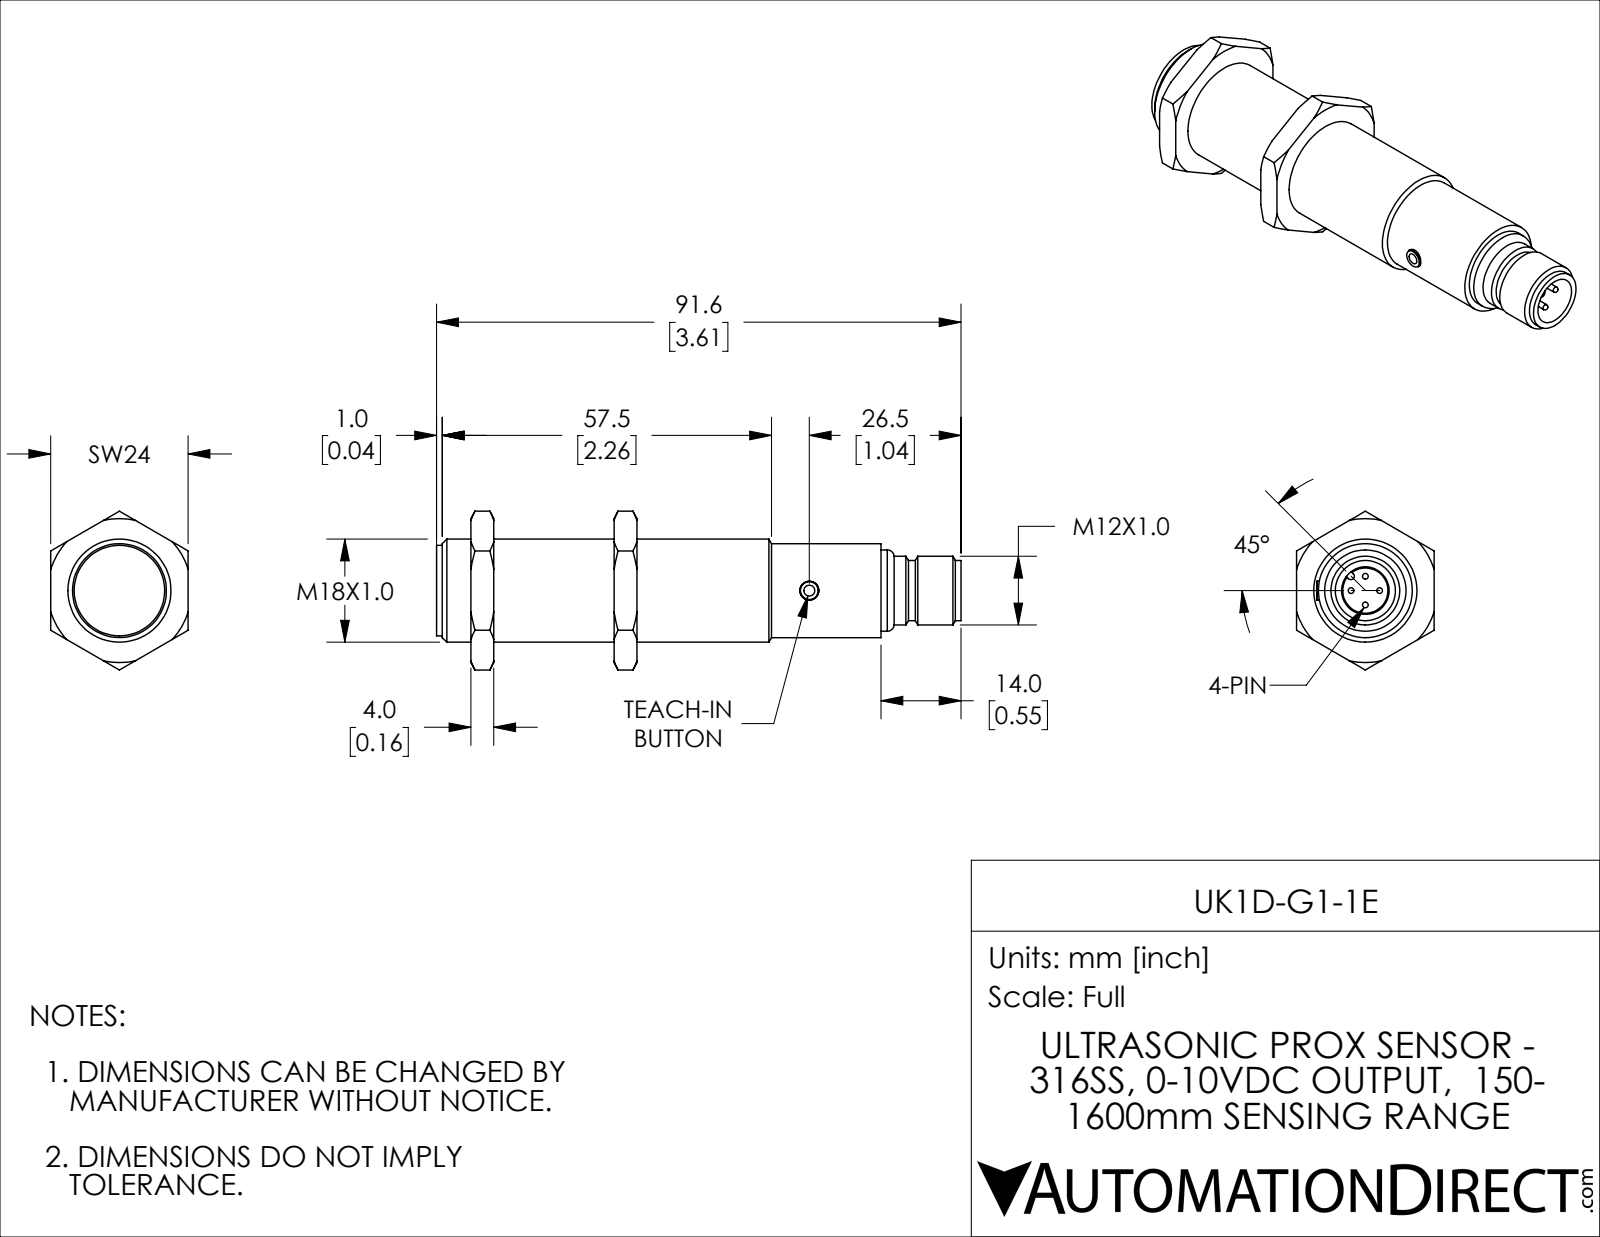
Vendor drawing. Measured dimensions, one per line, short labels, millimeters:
name: UK1D-G1-1E
written by: SolidWorks 2018 (AUTOMOTIVE_DESIGN)
unit: mm
bodies: 4 solids, 113 faces (27 planar, 35 cylindrical, 51 other)
size: 91.6 × 27.7 × 24
volume: 21 930 mm³; area: 7 723 mm²
holes: 1× ⌀3.3, 1× ⌀8.3, 1× ⌀18
bosses: 4× ⌀1, 1× ⌀16.4, 1× ⌀15.8, 1× ⌀14.2, 1× ⌀12, 1× ⌀10.5
rounds: 1× R0.6
face distances: 25, 4, 24, 29, 21, 6, 10, 31, 35, 77.6
